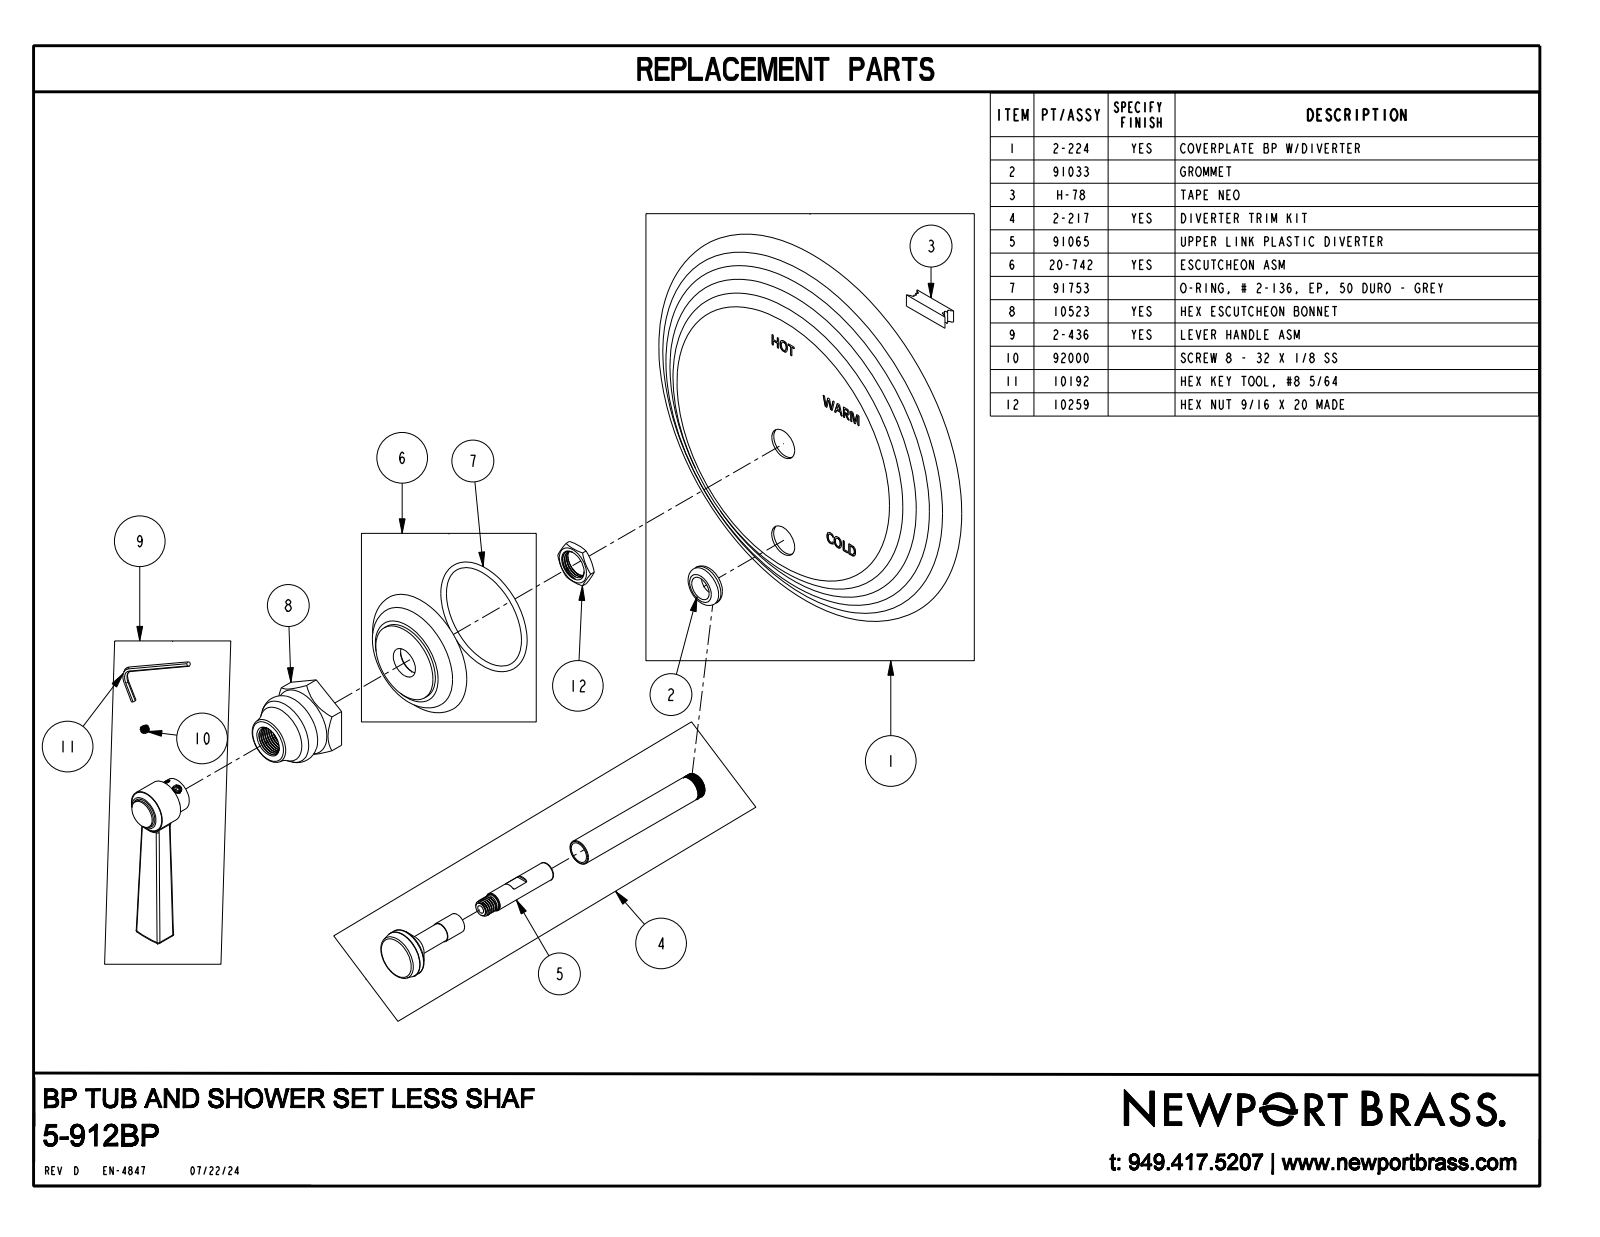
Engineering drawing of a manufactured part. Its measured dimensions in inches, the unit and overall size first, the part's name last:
Units: inches
Overall size (bounding box): 7.75 × 7.75 × 3.359
Round bosses / shafts (diameter × count): ⌀1.482 ×1, ⌀0.9 ×1, ⌀0.8 ×1, ⌀0.625 ×1, ⌀0.525 ×1, ⌀0.472 ×1, ⌀0.4 ×1, ⌀0.354 ×1
Partial cylindrical surfaces — rounded edges, fillets, slot ends (radius × count): R0.04 ×2, R0.055 ×2
Main face-to-face distances: 0.754, 1.313, 1.927, 1.173, 2.441, 1.687, 0.514, 1.129, 0.375, 0.798
Volume: 31.67 in³ · Surface area: 117.1 in²
Bodies: 1 solid, 284 faces (130 planar, 20 cylindrical, 134 other)
Part name (STEP PRODUCT): 5-912BP
STEP written by: CREO PARAMETRIC BY PTC INC, 2018400 (CONFIG_CONTROL_DESIGN)
